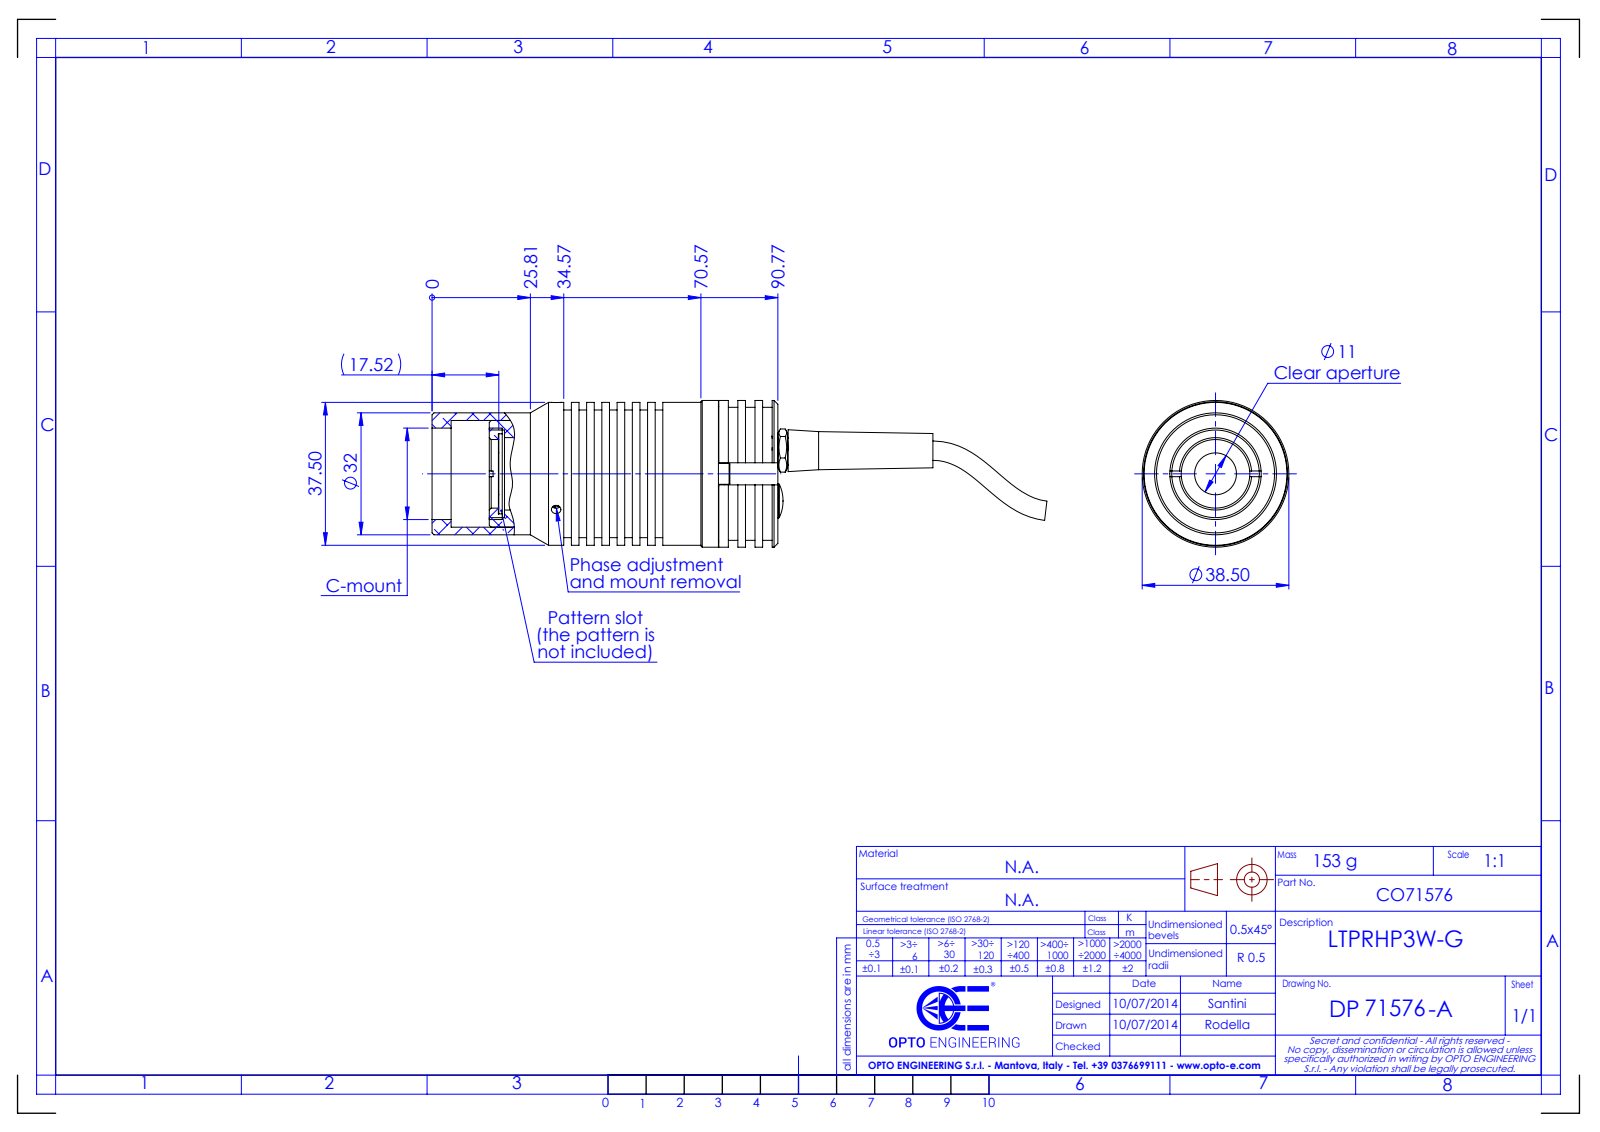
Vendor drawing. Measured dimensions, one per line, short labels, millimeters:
name: DP71576-A_LTPRHP3W-G
written by: SolidWorks 2021 (CONFIG_CONTROL_DESIGN)
unit: mm
bodies: 0 solids, 236 faces (89 planar, 93 cylindrical, 54 other)
size: 161.4 × 38.5 × 38.5
holes: 3× ⌀2.5, 3× ⌀4, 1× ⌀24, 1× ⌀28
bosses: 3× ⌀5.5, 1× ⌀38.5, 1× ⌀37.5, 1× ⌀34.9, 1× ⌀33.5, 1× ⌀32, 1× ⌀9
rounds: 3× R2.9, 2× R3.4
face distances: 2, 4, 6, 10, 8, 12, 14, 16, 18, 20
hole spacings: 15.25, 26.41, 26.42
